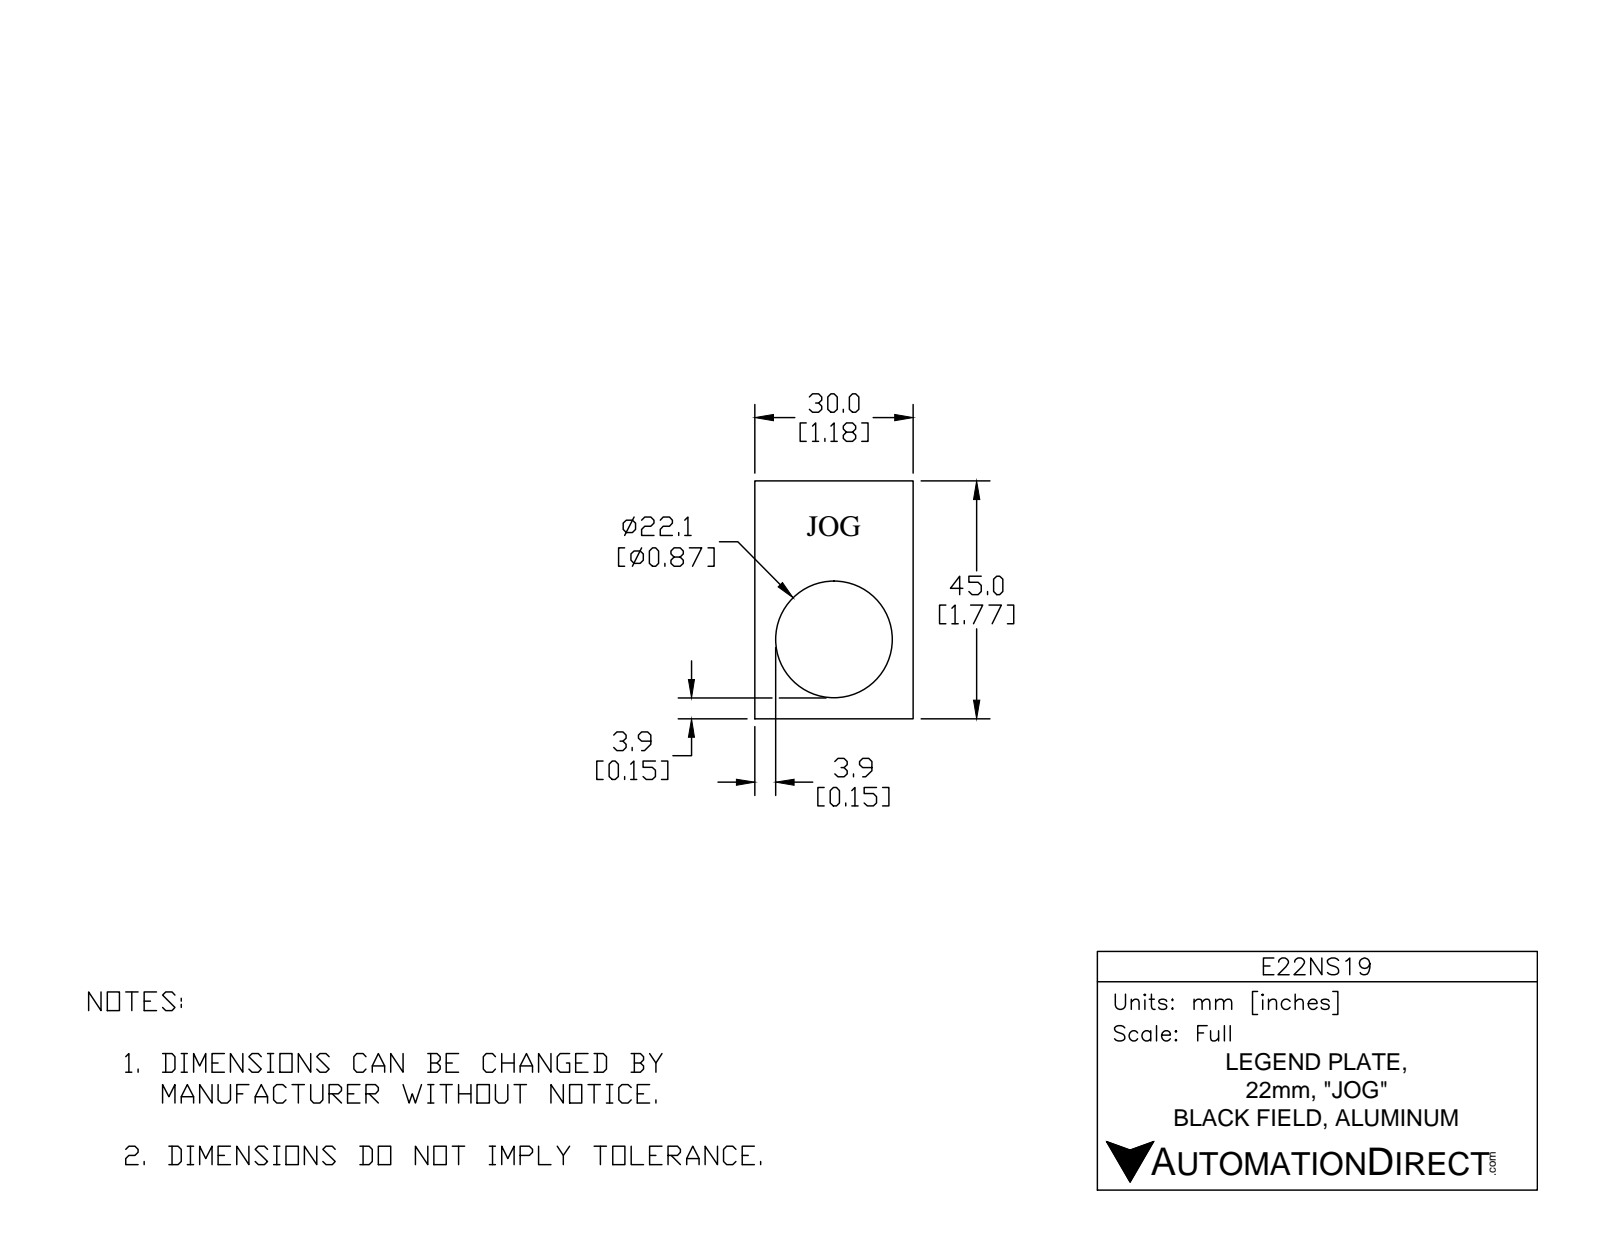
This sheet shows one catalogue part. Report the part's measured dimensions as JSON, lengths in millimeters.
{"part_name": "E22NS19", "step_written_by": "SolidWorks 2017 (AUTOMOTIVE_DESIGN)", "units": "millimeters", "bodies": {"solids": 1, "faces": 46, "planar": 21, "cylindrical": 3, "other": 22}, "overall_size": [45, 30, 1.3], "volume_mm3": 1252, "surface_area_mm2": 2233, "round_holes": [[22.2, 1]], "face_to_face_distances": [1.3, 30, 45, 1.05, 4.7, 40.3, 13.4, 16.6, 3.2, 11]}
